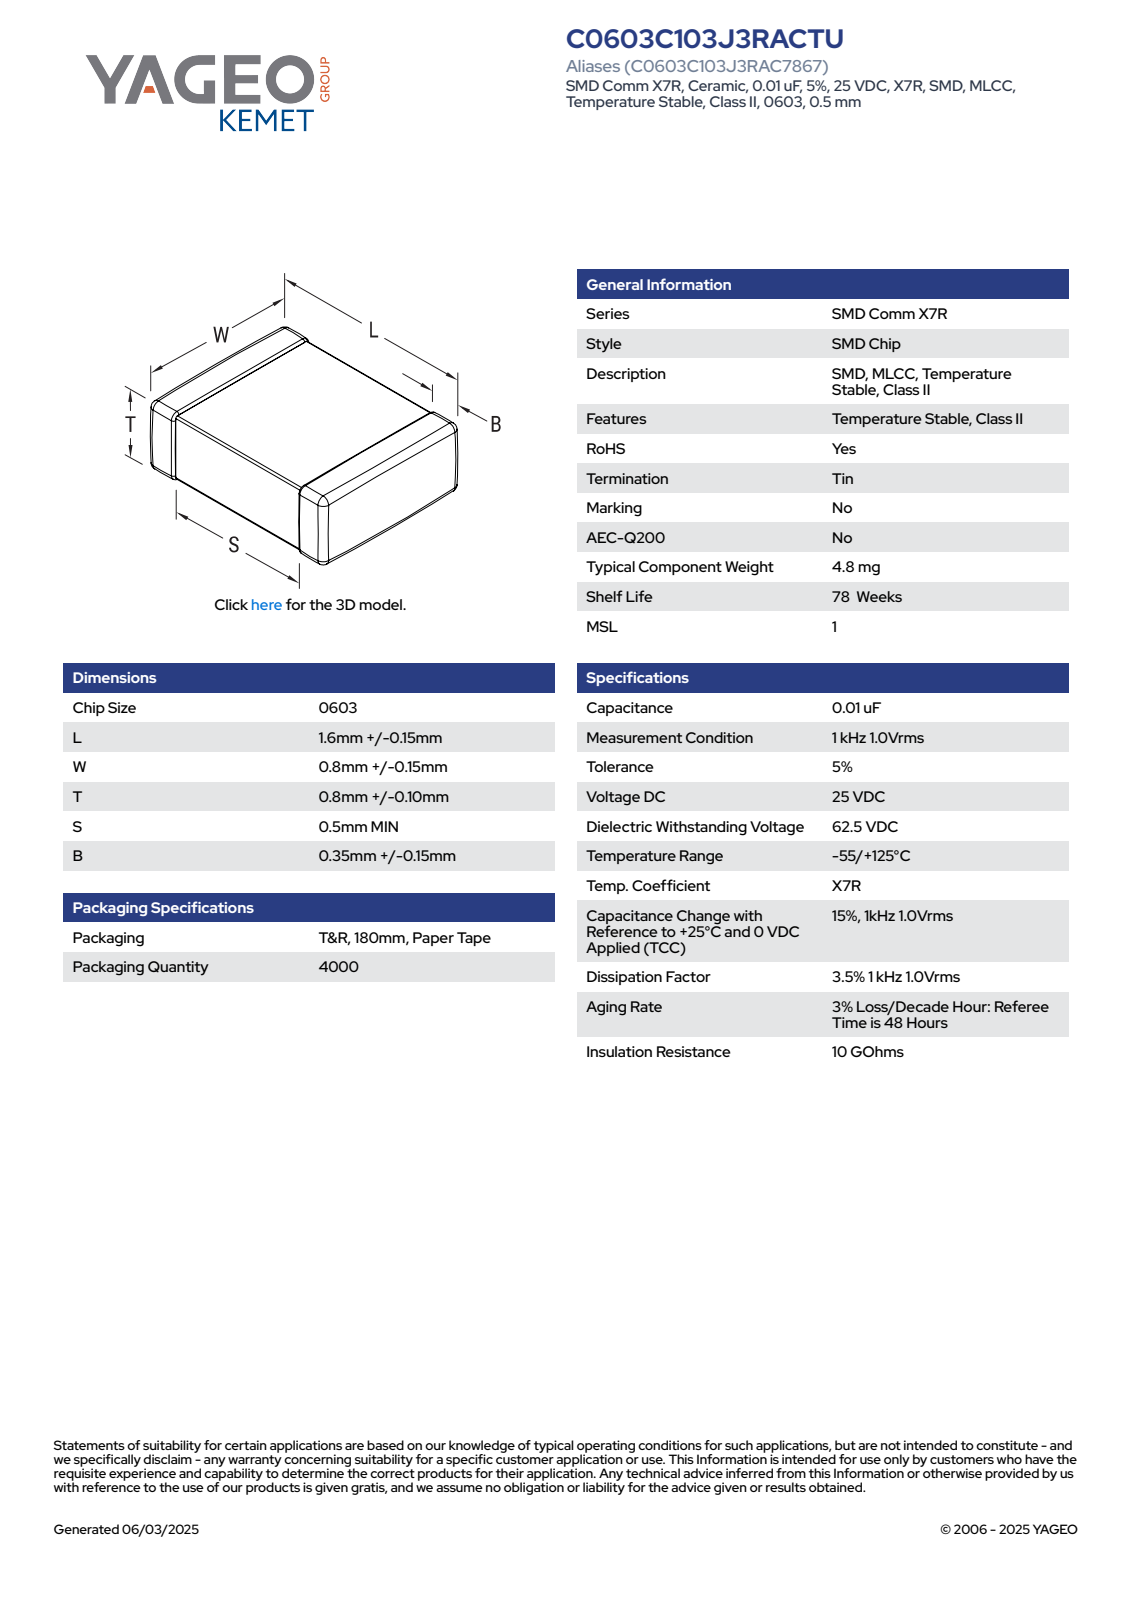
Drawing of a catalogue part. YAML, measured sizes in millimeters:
part_name: "CCS_CCSTD_0603_L1.75W0.95T0.9B0.35"
step_written_by: "SolidWorks 2021 (AUTOMOTIVE_DESIGN)"
units: millimeters
bodies: {solids: 4, faces: 125, planar: 71, cylindrical: 38, other: 16}
overall_size: [1.75, 0.95, 0.9]
volume: 1
surface_area: 8
face_to_face_distances: [0.88, 0.93, 0.9, 0.95, 1.75, 0.86, 0.91, 0.89, 0.87, 0.81]
